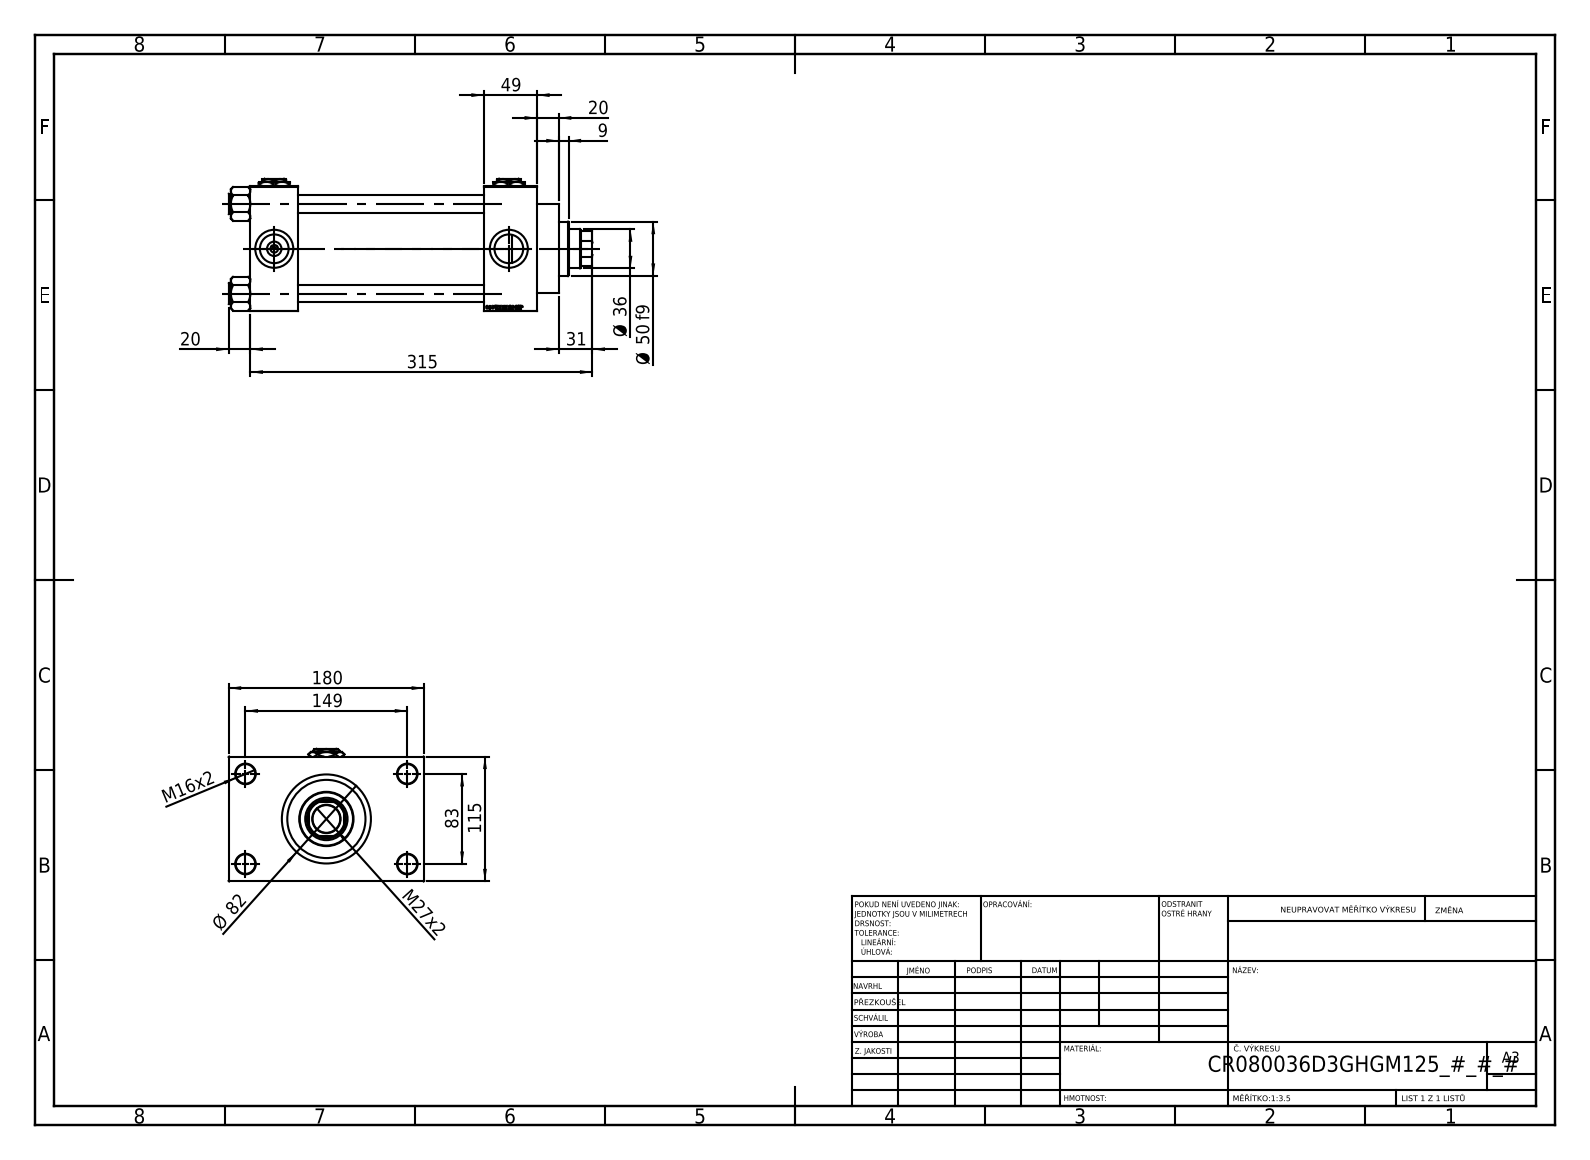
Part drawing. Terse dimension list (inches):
name: Zatka_pro_OIL_PORT; NUT_M5_D; V215CR_VCP_D; V215CR_D_Body (+2 more)
written by: SolidWorks 2019 (CONFIG_CONTROL_DESIGN)
unit: in
bodies: 13 solids, 1252 faces (593 planar, 99 cylindrical, 560 other)
size: 13.189 × 7.087 × 4.803
volume: 136.6 in³; area: 606.1 in²
holes: 4× ⌀0.63, 4× ⌀0.709, 4× ⌀1.041, 4× ⌀1.378, 3× ⌀0.276, 1× ⌀1.004, 1× ⌀1.417, 1× ⌀1.535, 1× ⌀2.402, 1× ⌀2.835, 1× ⌀3.15
bosses: 4× ⌀0.748, 1× ⌀3.386, 1× ⌀3.228, 1× ⌀1.969
rounds: 1× R0.689
face distances: 4.528, 6.732, 8.661, 1.929, 1.732, 8.465, 10.394, 1.28, 5.807, 7.087
hole spacings: 1.305, 2.302, 3.256, 3.357, 3.513, 4.561, 5.607, 3.268
